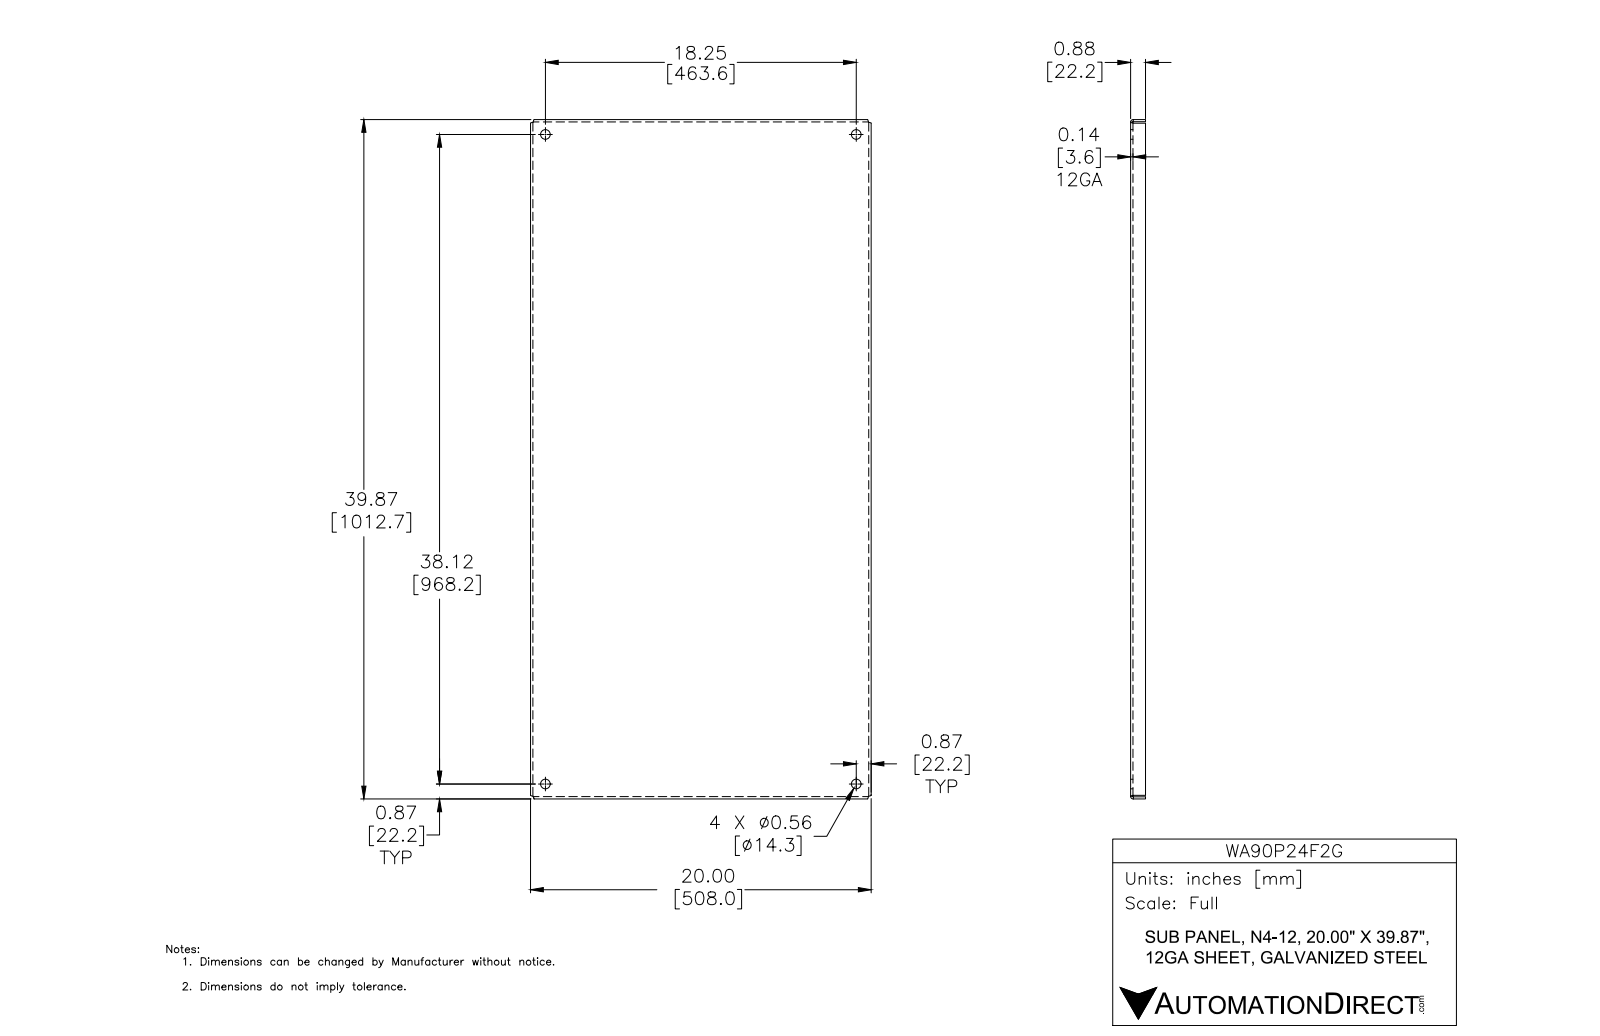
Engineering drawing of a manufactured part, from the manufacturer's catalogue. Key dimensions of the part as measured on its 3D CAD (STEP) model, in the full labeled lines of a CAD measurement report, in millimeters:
Part name (STEP PRODUCT): WA_P_F_G
STEP written by: Autodesk Inventor 2012 (AUTOMOTIVE_DESIGN)
Units: millimetres
Bodies: 1 solid, 42 faces (22 planar, 12 cylindrical, 8 other)
Overall size (bounding box): 1013 × 508 × 22.2
Volume: 1 361 000 mm³ · Surface area: 1 151 000 mm²
Round holes (diameter × count): ⌀14.3 ×4
Partial cylindrical surfaces — rounded edges, fillets, slot ends (radius × count): R0.4 ×4, R2.8 ×4
Main face-to-face distances: 2.4, 505.6, 508, 503.3, 1010.6, 1013, 1008.2, 19.8, 22.2, 4.1
Hole centre spacings: 463.6, 968.5, 1073.7
